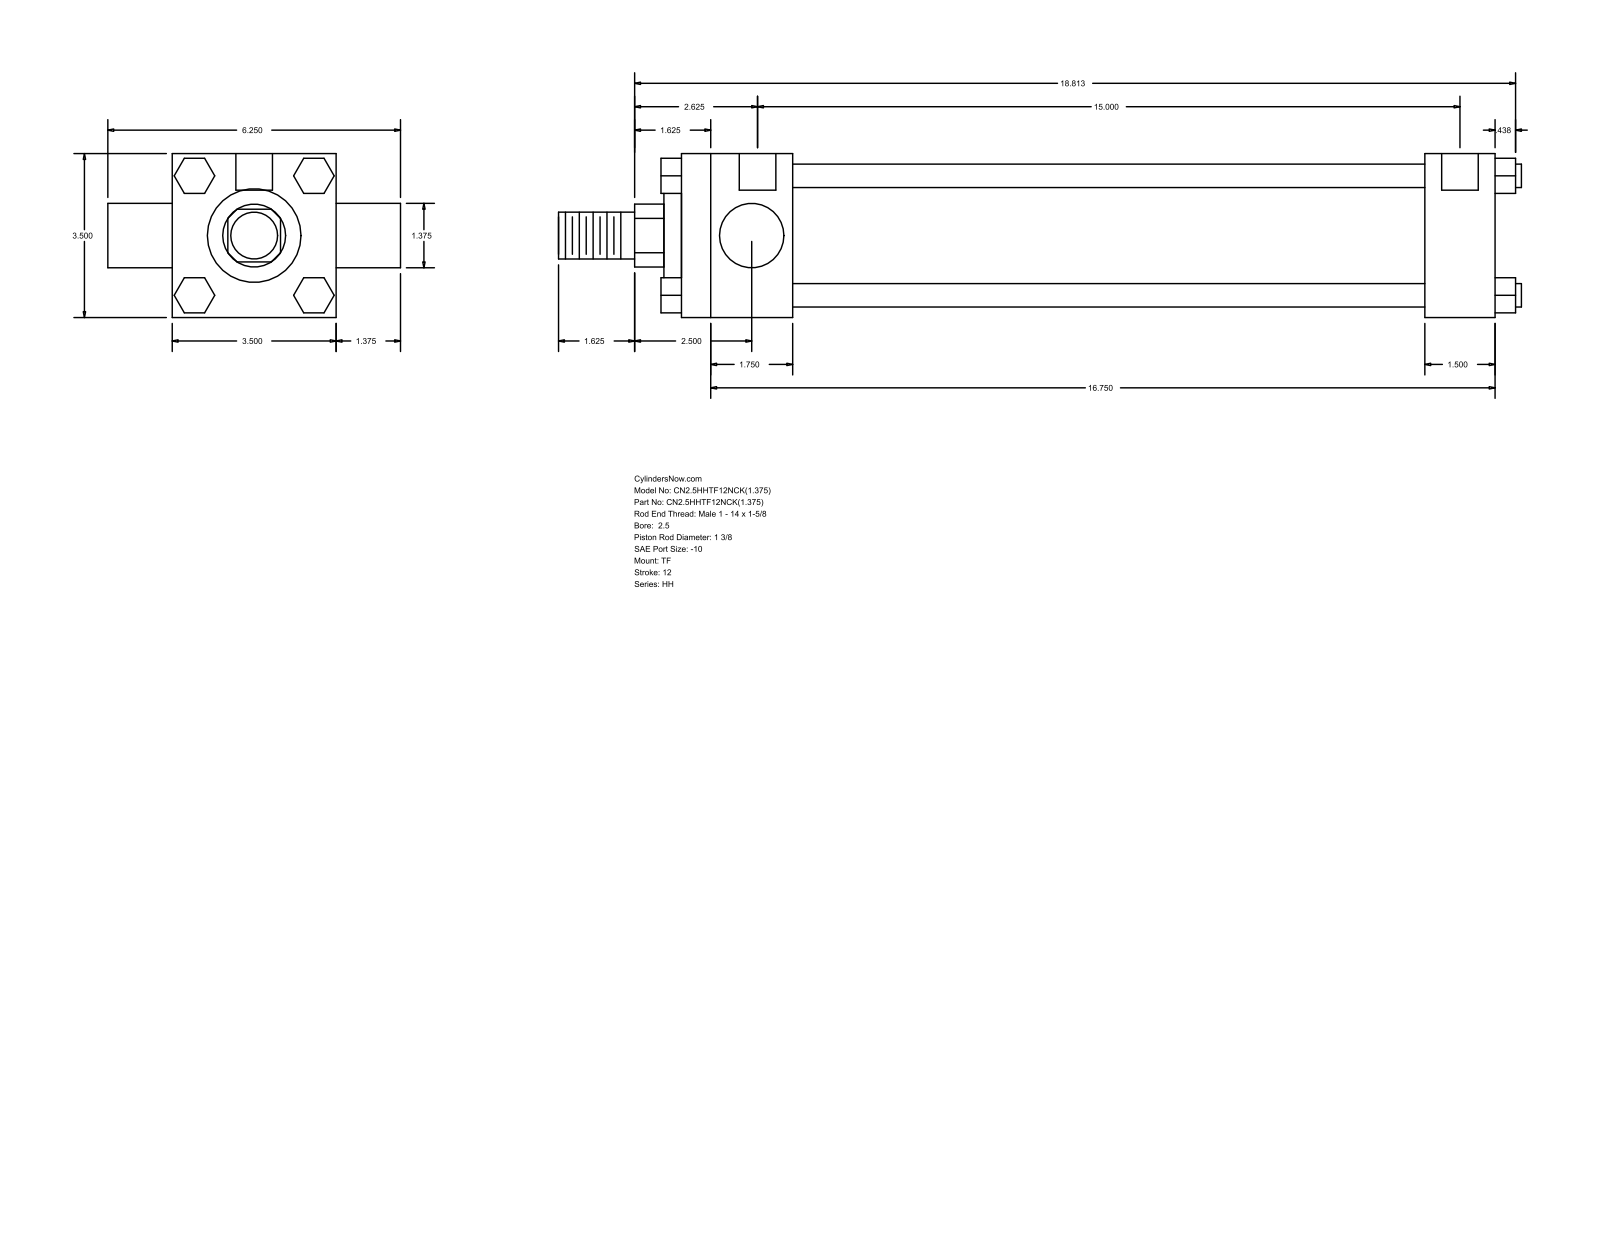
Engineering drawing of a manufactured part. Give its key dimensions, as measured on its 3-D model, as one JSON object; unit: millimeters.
{"part_name": "HH_TF__0250_1.375", "step_written_by": "GSSL Pune (CONFIG_CONTROL_DESIGN)", "units": "millimeters", "bodies": {"solids": 0, "faces": 120, "planar": 92, "cylindrical": 28, "other": 0}, "overall_size": [522.29, 158.75, 88.9], "round_holes": [[5.56, 3], [19.84, 2]], "round_bosses_or_shafts": [[12.7, 4], [34.92, 2], [73.03, 1], [50.8, 1], [25.4, 1]], "partial_cylinders_radius": [[17.06, 1]], "face_to_face_distances": [88.9, 441.33, 60.32, 381.01, 403.22, 342.9, 38.11, 19.05, 32.38, 56.09], "hole_center_spacings": [1.58, 382.59, 381.01, 384.17]}
